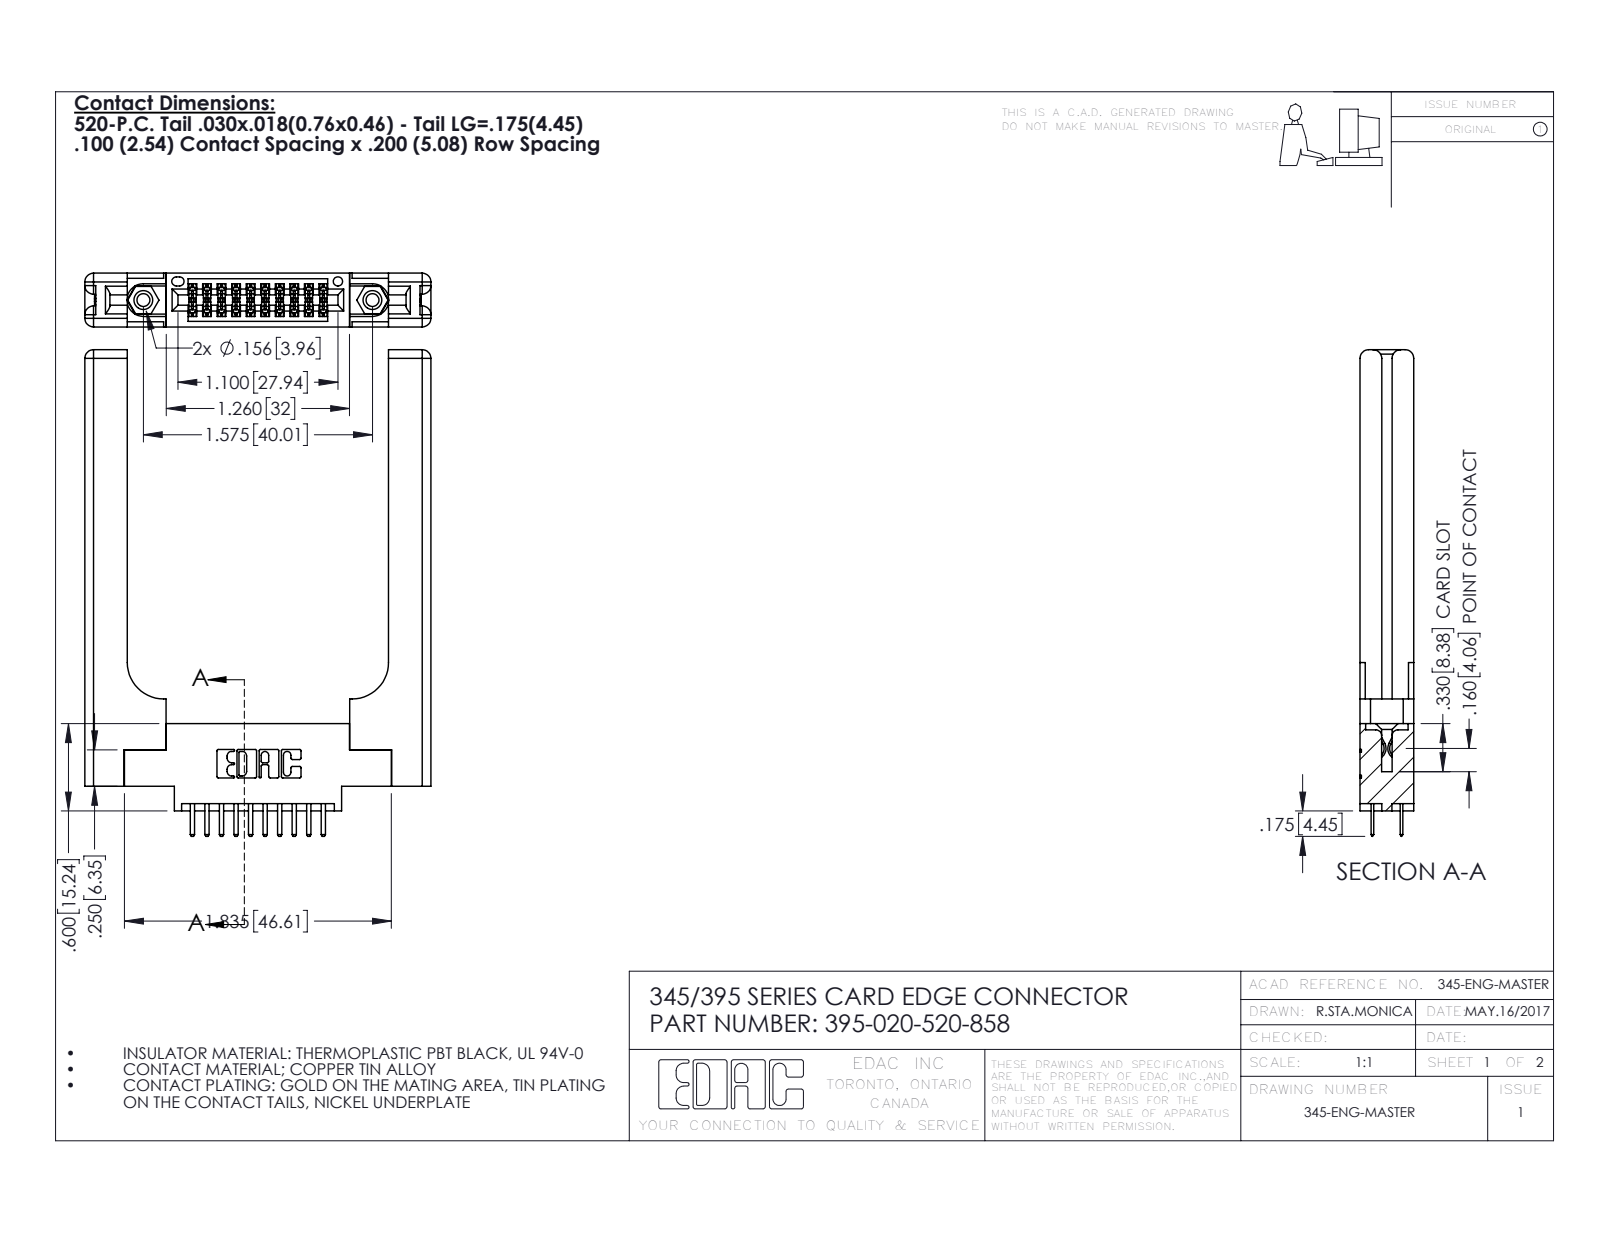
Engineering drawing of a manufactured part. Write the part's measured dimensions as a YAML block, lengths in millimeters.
part_name: "345 Part_0.170 Offset - 0.156 Dia-TH; 395-020-520-858; 345-292-001_345-293-120; 345-250-001_345-250-001-102 (+1 more)"
step_written_by: "SolidWorks 2016 (CONFIG_CONTROL_DESIGN)"
units: millimeters
bodies: {solids: 25, faces: 1466, planar: 932, cylindrical: 474, other: 60}
overall_size: [85, 60.4, 9.4]
volume: 13900
surface_area: 12620
round_holes:
  - {diameter: 2.3, count: 2}
  - {diameter: 3.2, count: 2}
  - {diameter: 4, count: 2}
  - {diameter: 1.6, count: 1}
round_bosses_or_shafts:
  - {diameter: 3.9, count: 2}
partial_cylinders:
  - {radius: 0.2, count: 30}
  - {radius: 0.3, count: 24}
  - {radius: 0.3, count: 22}
  - {radius: 1.5, count: 16}
  - {radius: 0.2, count: 6}
  - {radius: 0.8, count: 6}
  - {radius: 0.7, count: 3}
  - {radius: 0.4, count: 2}
face_to_face_distances: [9.4, 1.8, 3.8, 5.6, 7.6, 2, 3.8, 45.6, 5.7, 5.1]
hole_center_spacings: [6.9, 34.1, 40]
